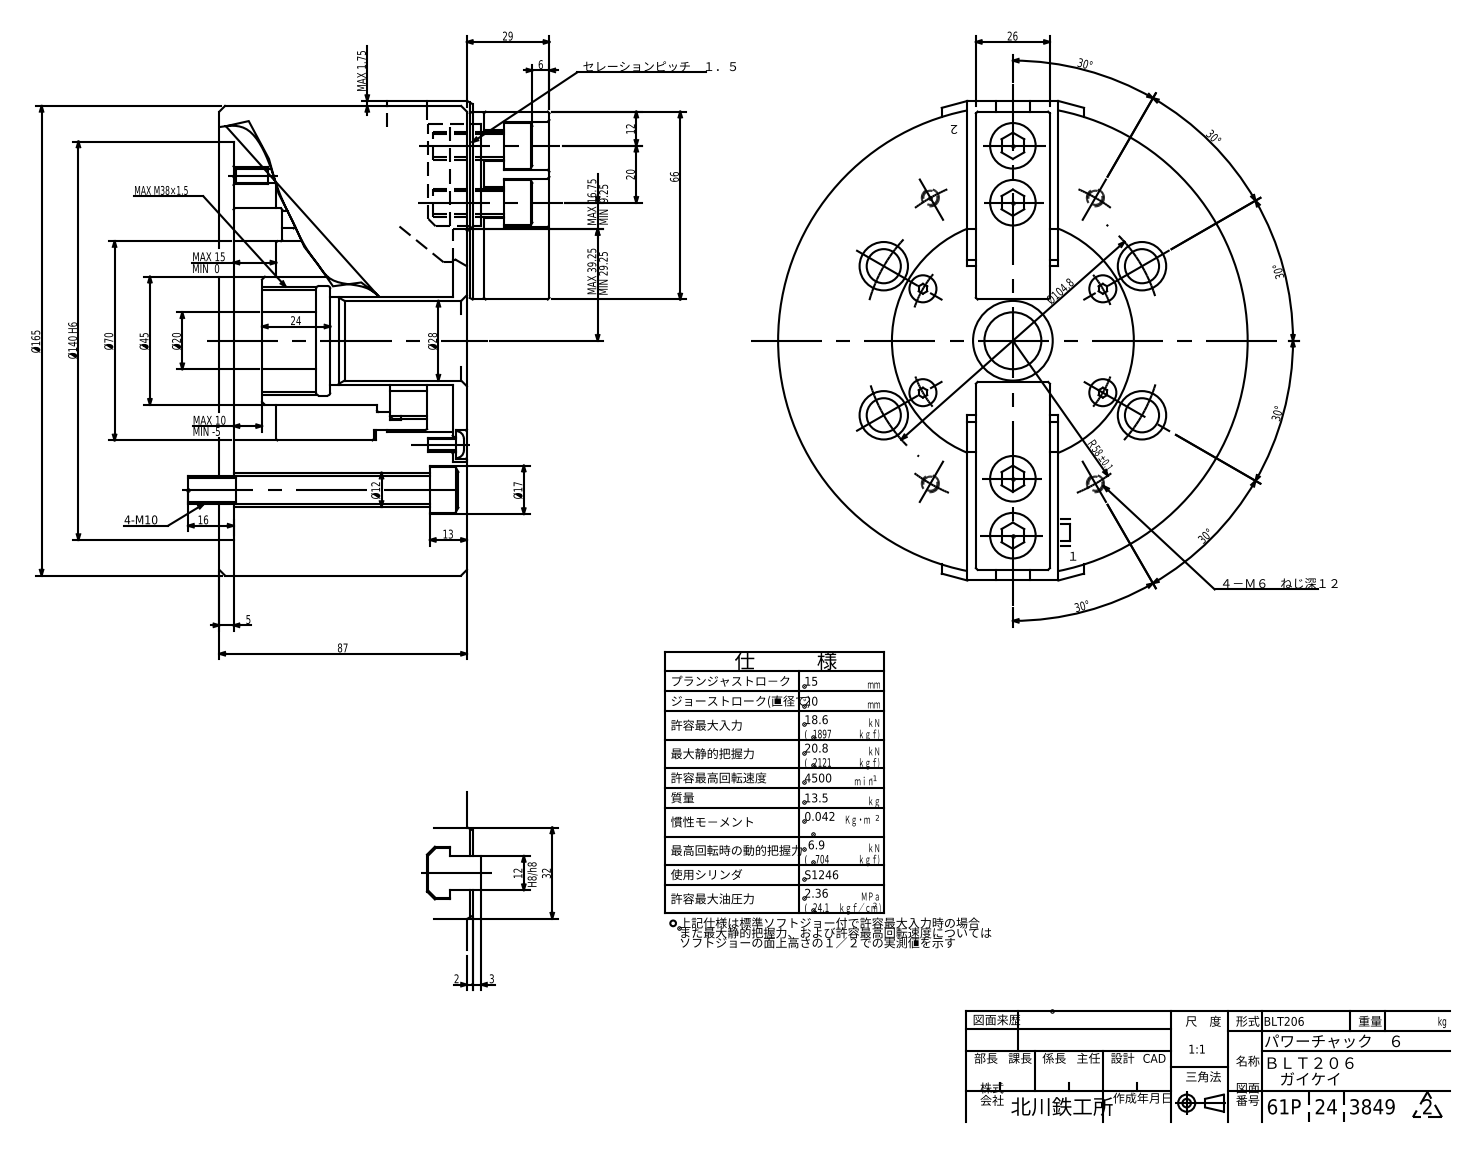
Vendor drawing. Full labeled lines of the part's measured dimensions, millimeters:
Part name (STEP PRODUCT): BLT206-Solid
STEP written by: ST-DEVELOPER v16.7 (AUTOMOTIVE_DESIGN)
Units: millimetres
Bodies: 1 solid, 1687 faces (1181 planar, 352 cylindrical, 154 other)
Overall size (bounding box): 165 × 165 × 127.2
Volume: 1 710 000 mm³ · Surface area: 187 590 mm²
Round holes (diameter × count): ⌀17 ×8, ⌀8.5 ×5, ⌀4.2 ×4, ⌀5.2 ×4, ⌀5.5 ×4, ⌀10 ×4, ⌀11 ×4, ⌀12 ×4, ⌀20 ×1, ⌀28 ×1, ⌀31 ×1, ⌀35.5 ×1
Round bosses / shafts (diameter × count): ⌀16 ×8, ⌀9.73 ×8, ⌀9.5 ×4, ⌀4.83 ×4, ⌀165 ×1, ⌀63 ×1, ⌀55 ×1
Partial cylindrical surfaces — rounded edges, fillets, slot ends (radius × count): R0.1 ×62, R0.8 ×4, R5 ×2, R6.5 ×2, R9.25 ×2, R0.51 ×1, R2.19 ×1, R4.08 ×1
Main face-to-face distances: 82, 5, 87, 7.5, 34.2, 19, 60.5, 26, 65.5, 74.5
Hole centre spacings: 68.53, 78.17, 36.5, 52.4, 58, 15.9, 29.08, 29.77
